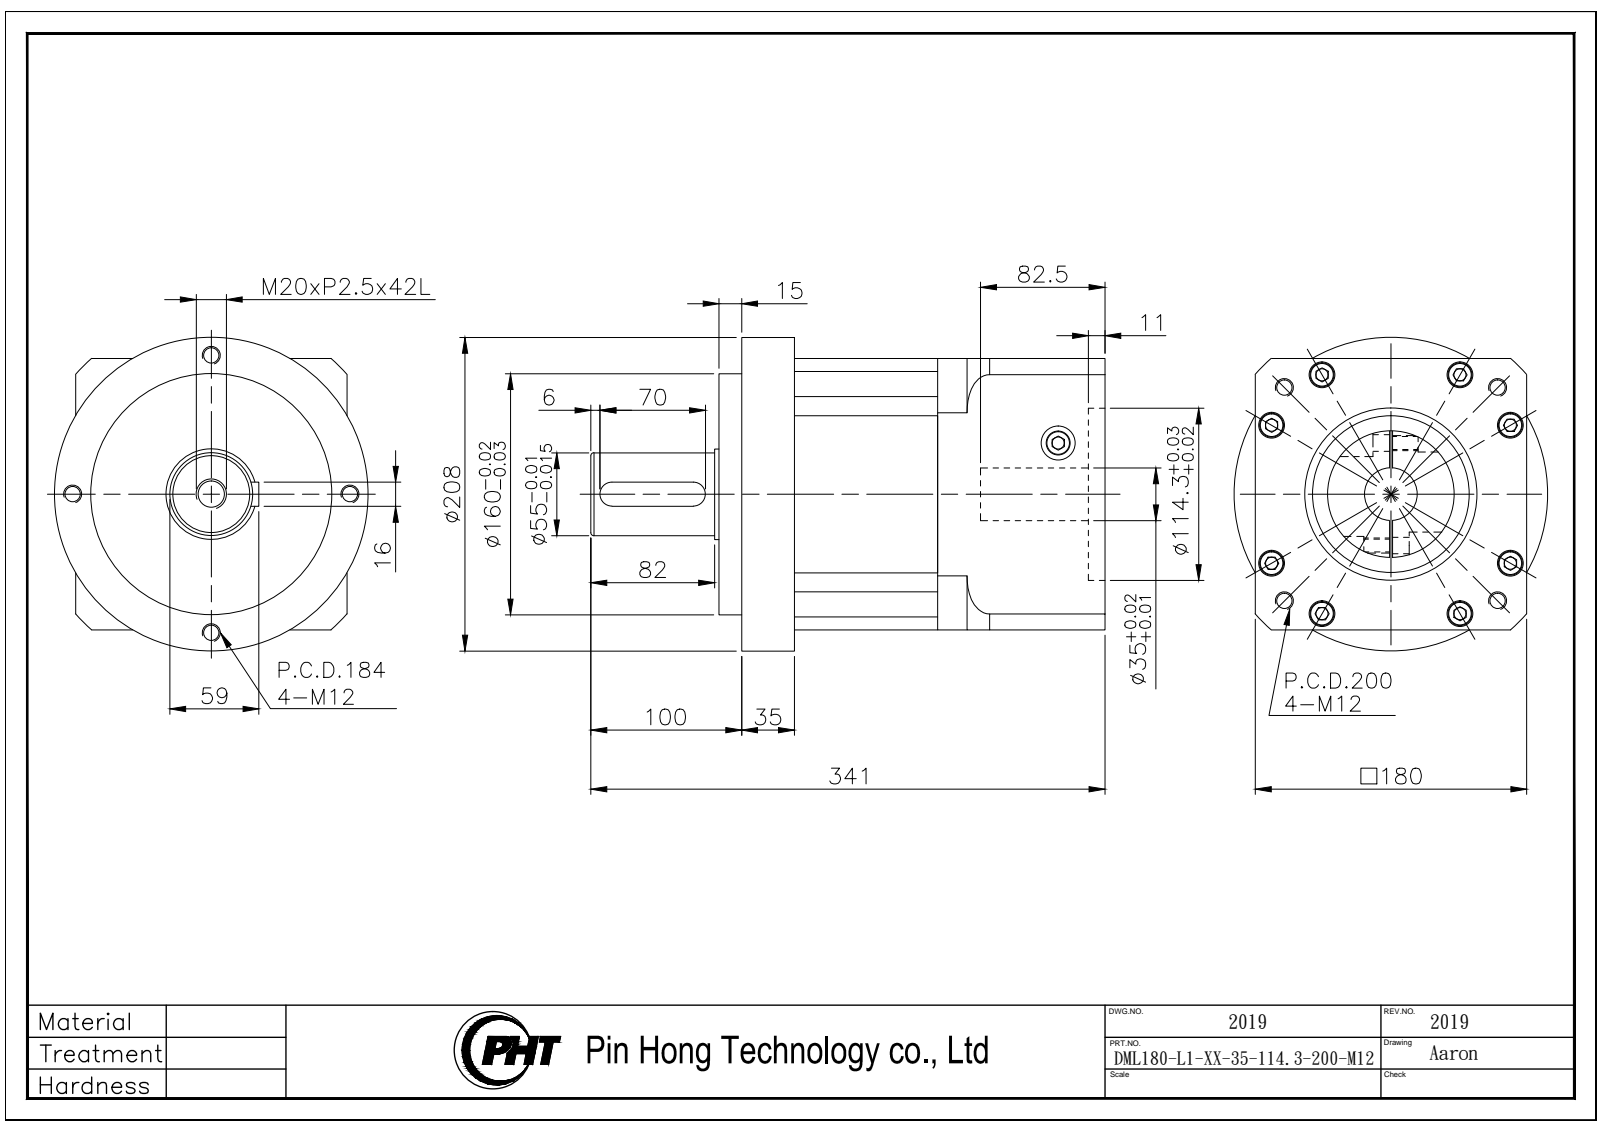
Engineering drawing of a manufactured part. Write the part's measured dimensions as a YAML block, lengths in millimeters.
part_name: "DML180-L1-XX-35-114.3-200-M12_2019"
step_written_by: "SolidWorks 2016 (AUTOMOTIVE_DESIGN)"
units: millimeters
bodies: {solids: 3, faces: 261, planar: 108, cylindrical: 113, other: 40}
overall_size: [341, 208, 208]
volume: 7415000
surface_area: 493793
round_holes:
  - {diameter: 10.2, count: 8}
  - {diameter: 11, count: 8}
  - {diameter: 17, count: 8}
  - {diameter: 22.5, count: 2}
  - {diameter: 17.5, count: 1}
  - {diameter: 35, count: 1}
  - {diameter: 104, count: 1}
  - {diameter: 114.3, count: 1}
round_bosses_or_shafts:
  - {diameter: 16, count: 8}
  - {diameter: 208, count: 1}
  - {diameter: 160, count: 1}
  - {diameter: 84, count: 1}
  - {diameter: 60, count: 1}
  - {diameter: 55, count: 1}
partial_cylinders:
  - {radius: 12.5, count: 4}
  - {radius: 8, count: 2}
  - {radius: 105, count: 1}
  - {radius: 120, count: 1}
face_to_face_distances: [95, 180, 111, 206, 50, 256, 145, 241, 130, 35]
hole_center_spacings: [91.5, 26.38, 47.5, 73.85, 91.75, 116.77, 129.4, 152.01]
